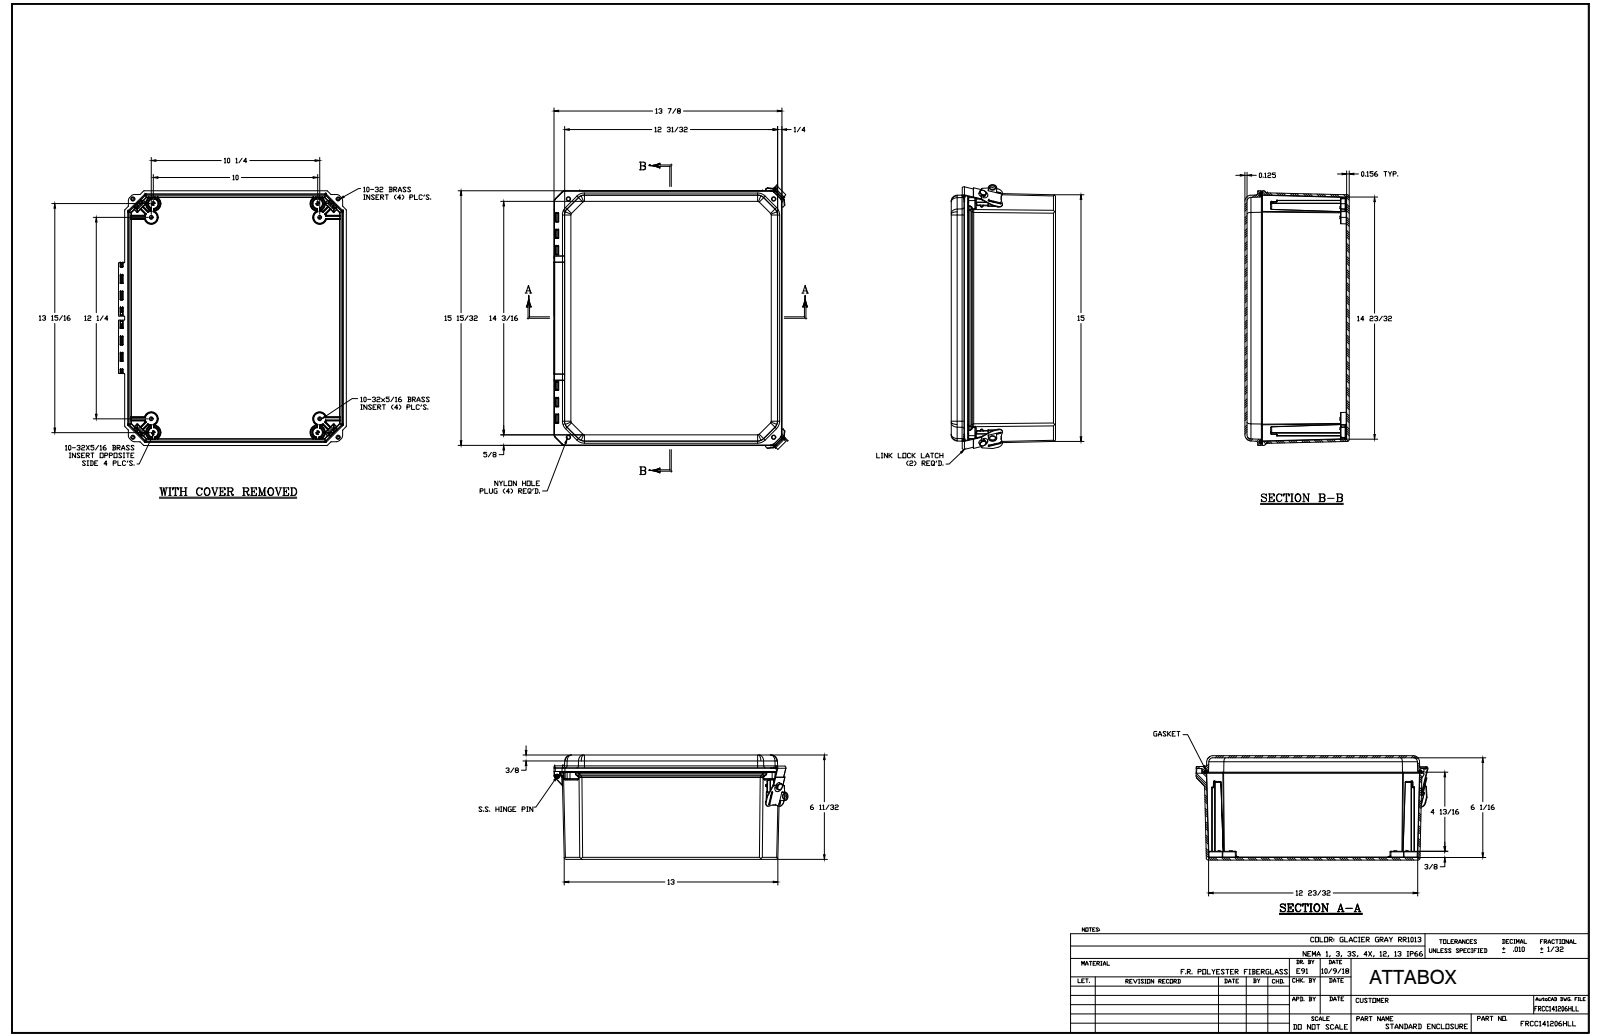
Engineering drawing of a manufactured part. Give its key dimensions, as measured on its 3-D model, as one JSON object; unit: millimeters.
{"part_name": "FRCC141206HLL", "step_written_by": "SolidWorks 2018 (AUTOMOTIVE_DESIGN)", "units": "millimeters", "bodies": {"solids": 33, "faces": 2380, "planar": 700, "cylindrical": 942, "other": 738}, "overall_size": [415.2, 363.1, 161.1], "volume_mm3": 1824000, "surface_area_mm2": 1034000, "round_holes": [[4, 12], [3.9, 8], [2.5, 4], [3.8, 4], [5.6, 4], [6.4, 4], [7.9, 4], [1.3, 2], [3, 2], [9.2, 2], [3.5, 1]], "round_bosses_or_shafts": [[6.2, 12], [22.1, 4], [5.3, 4], [5.1, 4], [3.4, 3], [15.2, 2], [1.3, 2]], "partial_cylinders_radius": [[0.3, 225], [0.1, 113], [0.5, 59], [3.2, 41], [0.8, 37], [1, 28], [6.4, 26], [0.8, 24]], "face_to_face_distances": [3.2, 4, 161.1, 157.1, 157.9, 154, 3.6, 3.5, 23.8, 134.1], "hole_center_spacings": [368, 340.8, 362.1, 10.9, 20.1, 21.4, 32.4, 40.2]}
